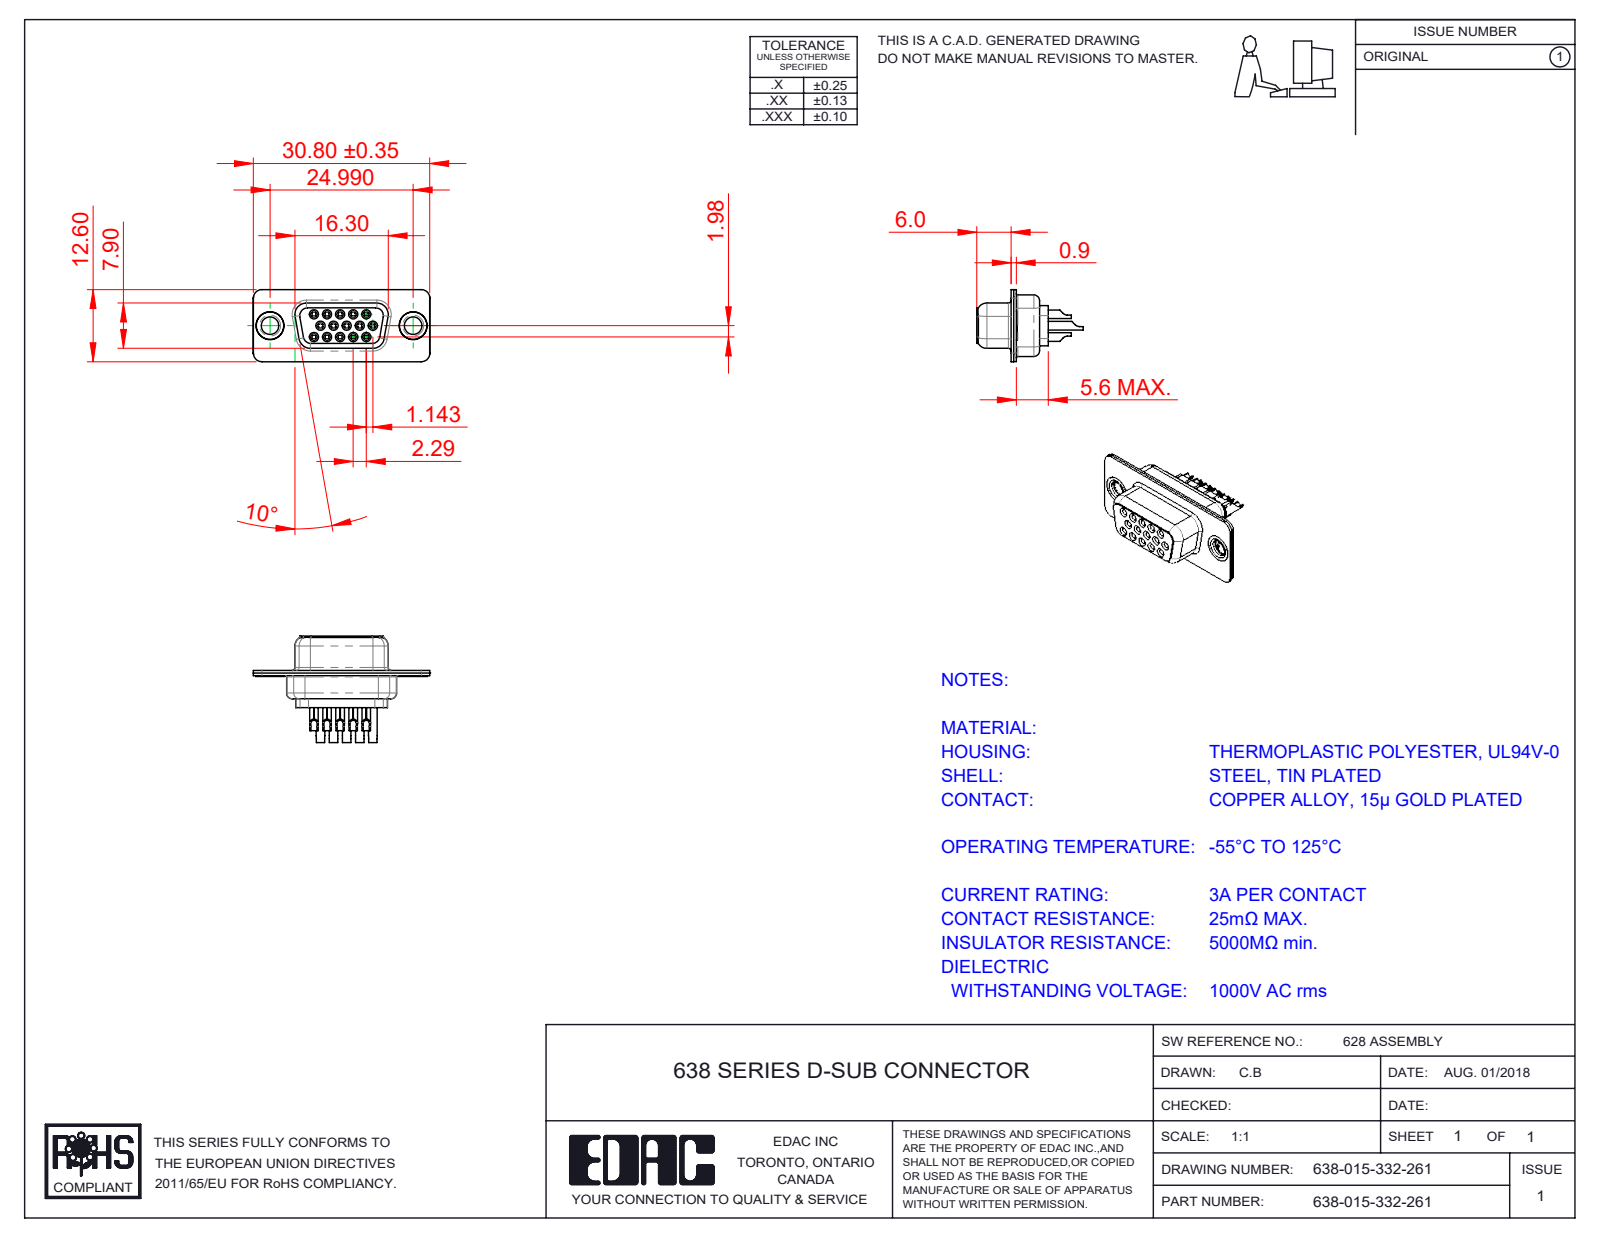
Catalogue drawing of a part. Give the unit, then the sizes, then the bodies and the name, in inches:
Units: inches
Overall size (bounding box): 1.213 × 0.732 × 0.496
Round holes (diameter × count): ⌀0.031 ×15, ⌀0.039 ×15, ⌀0.043 ×15, ⌀0.063 ×15, ⌀0.067 ×15, ⌀0.071 ×15, ⌀0.079 ×2, ⌀0.12 ×2, ⌀0.157 ×2, ⌀0.159 ×2, ⌀0.191 ×2
Round bosses / shafts (diameter × count): ⌀0.079 ×15, ⌀0.059 ×15, ⌀0.047 ×15, ⌀0.197 ×2, ⌀0.195 ×2, ⌀0.189 ×2, ⌀0.14 ×2
Partial cylindrical surfaces — rounded edges, fillets, slot ends (radius × count): R0.059 ×20, R0.079 ×12, R0.011 ×10, R0.061 ×8, R0.039 ×7, R0.053 ×5, R0.01 ×4, R0.02 ×4
Main face-to-face distances: 0.018, 0.035, 0.016, 0.056, 0.35, 0.26, 0.055, 0.09, 0.278, 0.033
Hole centre spacings: 0.156, 0.09, 0.18, 0.09, 0.238, 0.238, 0.27, 0.312
Volume: 0.093 in³ · Surface area: 8.858 in²
Bodies: 20 solids, 1588 faces (382 planar, 496 cylindrical, 710 other)
Part name (STEP PRODUCT): 638 Thru Hole Rivet; 638 Contact Row 2_32; 638 Shell Front_15 Contacts; 638 Contact Row 1_32 (+4 more)
STEP written by: SolidWorks 2020 (CONFIG_CONTROL_DESIGN)
